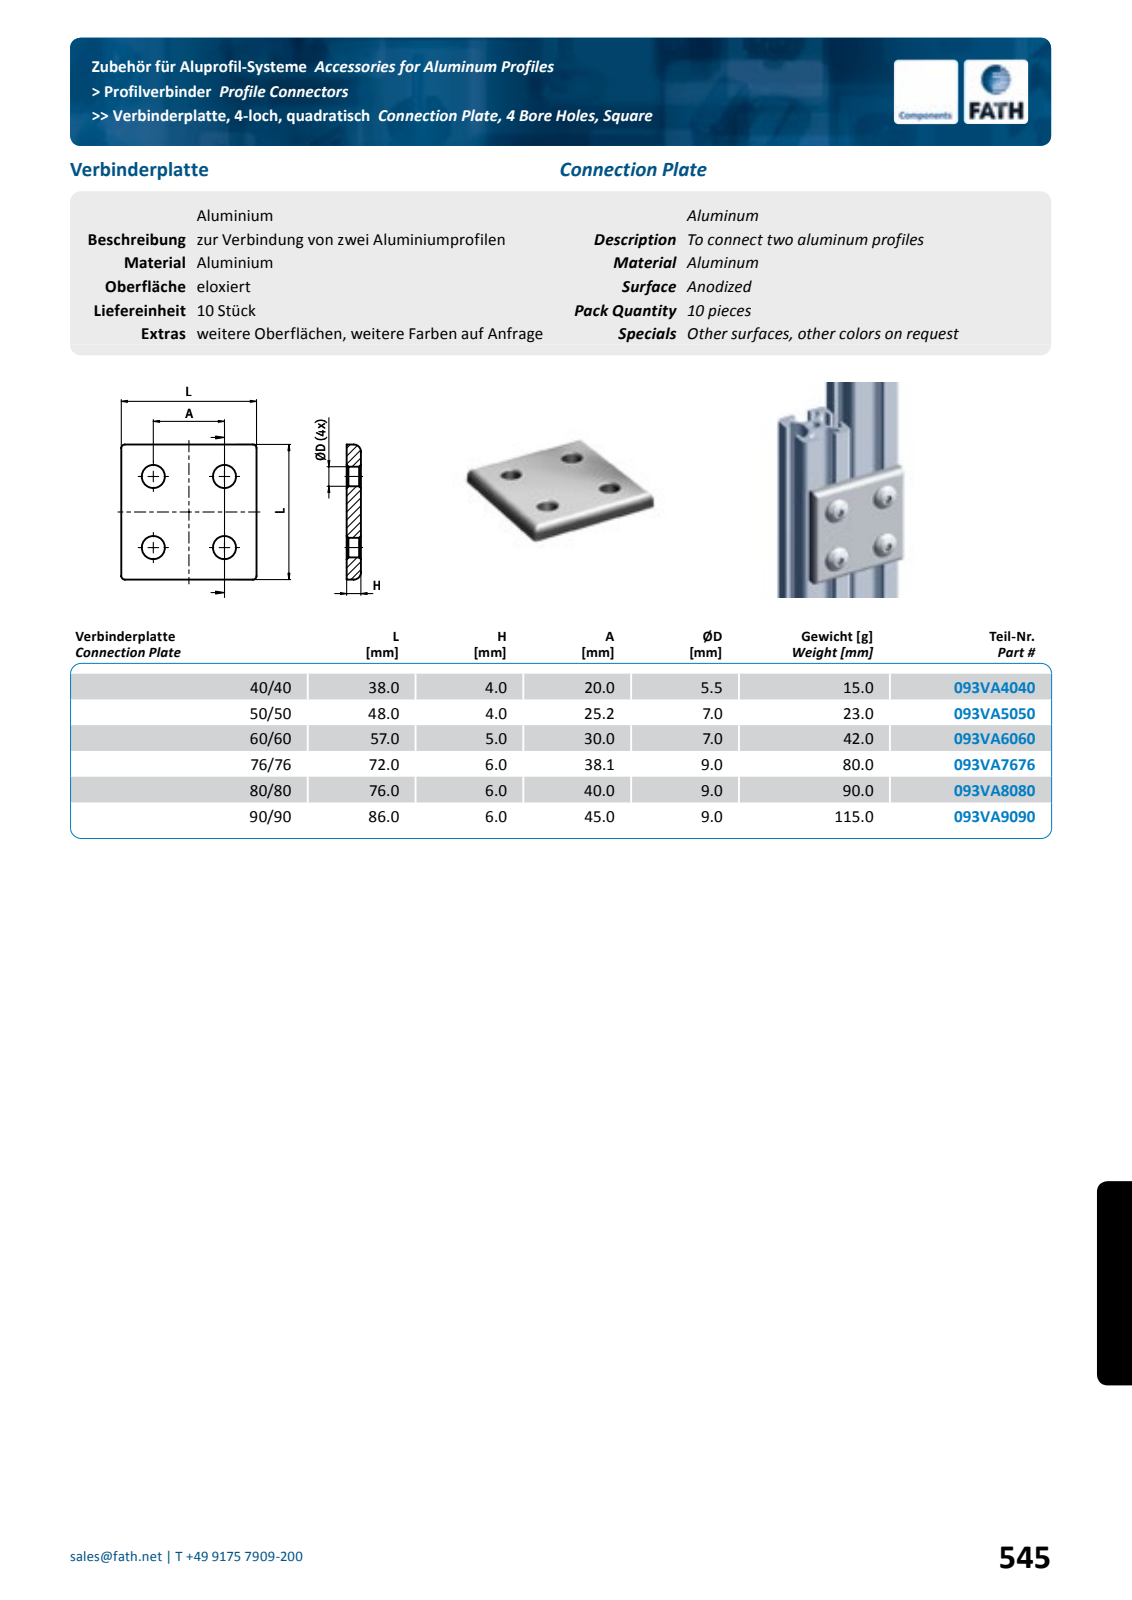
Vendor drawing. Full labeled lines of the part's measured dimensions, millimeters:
Part name (STEP PRODUCT): fath_093va8080
STEP written by: Spatial InterOp 3D (automotive_design)
Units: millimetres
Bodies: 1 solid, 42 faces (6 planar, 16 cylindrical, 20 other)
Overall size (bounding box): 76 × 76 × 6
Volume: 32 824 mm³ · Surface area: 13 195 mm²
Round holes (diameter × count): ⌀9 ×4
Partial cylindrical surfaces — rounded edges, fillets, slot ends (radius × count): R2 ×8
Main face-to-face distances: 6, 76
Hole centre spacings: 40, 56.57
